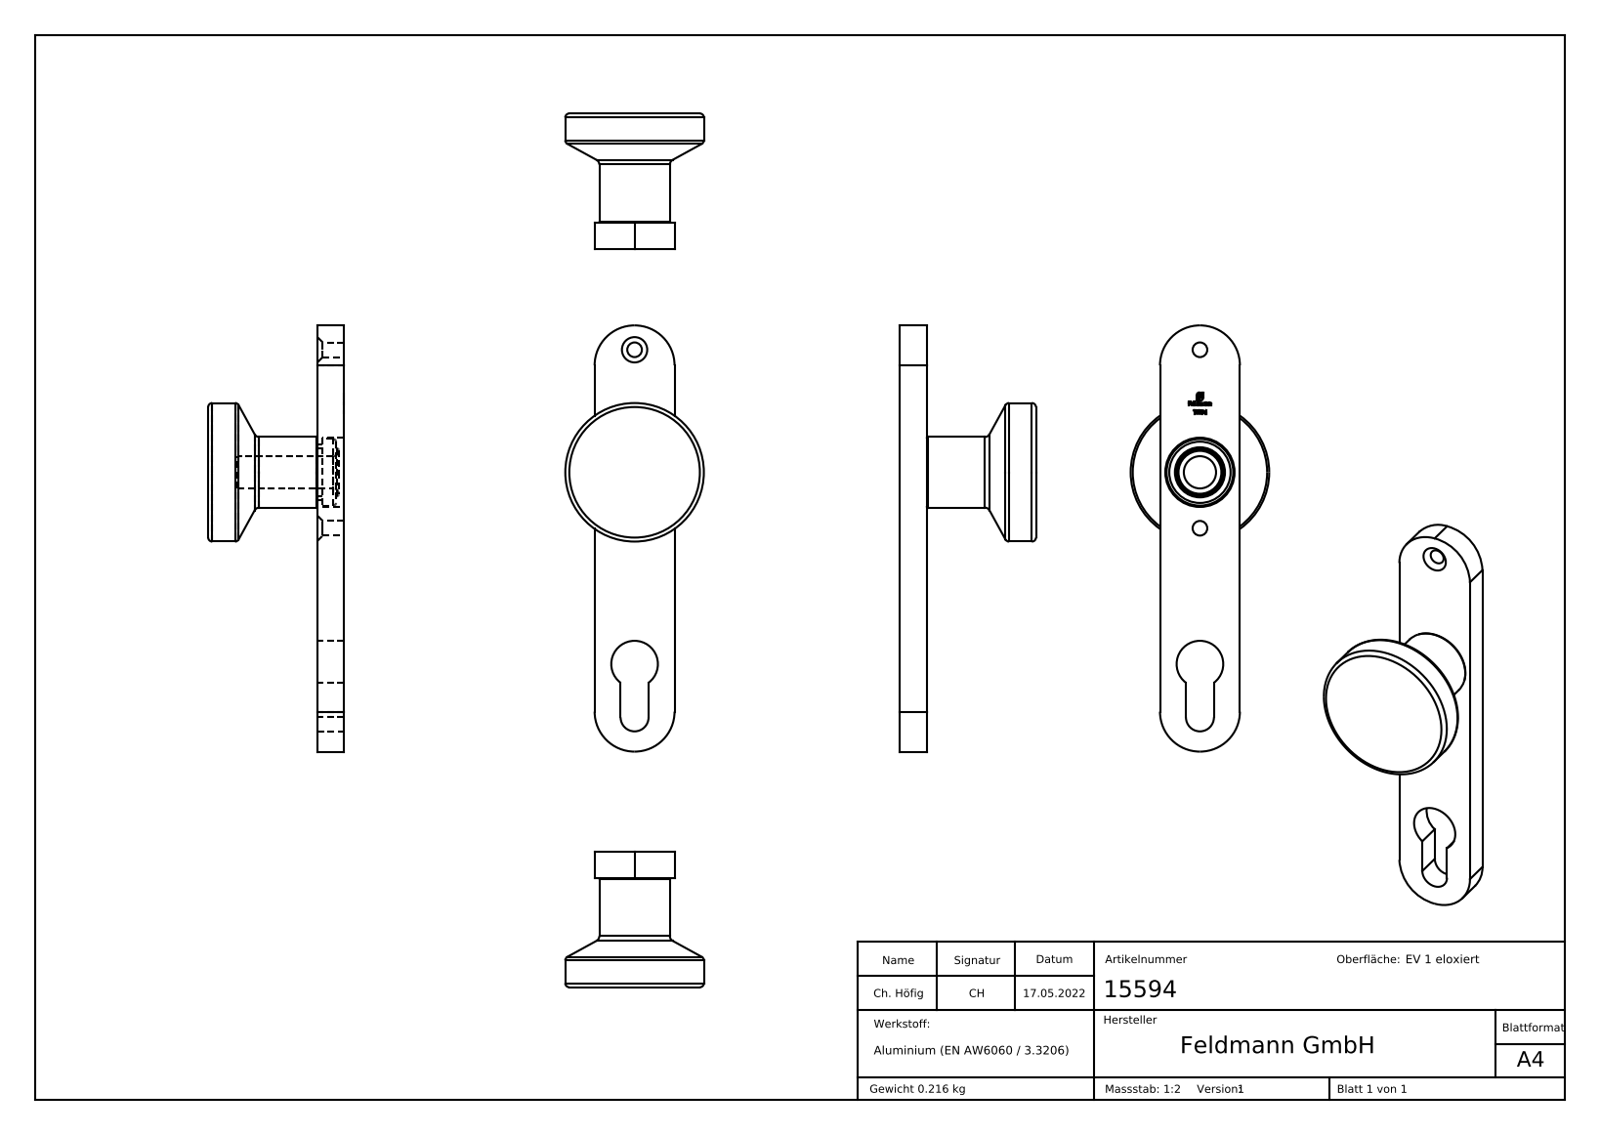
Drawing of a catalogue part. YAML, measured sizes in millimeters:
part_name: "15594 Teil1_15594 Teil1; 15594; 15594 Teil2_15594 Teil2"
step_written_by: "SolidWorks 2018 (CONFIG_CONTROL_DESIGN)"
units: millimeters
bodies: {solids: 2, faces: 261, planar: 142, cylindrical: 15, other: 104}
overall_size: [160, 52, 51]
volume: 79999
surface_area: 23536
round_holes:
  - {diameter: 5.5, count: 2}
  - {diameter: 12.1, count: 1}
  - {diameter: 17.5, count: 1}
  - {diameter: 21, count: 1}
  - {diameter: 26, count: 1}
round_bosses_or_shafts:
  - {diameter: 52, count: 1}
  - {diameter: 26.5, count: 1}
  - {diameter: 25, count: 1}
  - {diameter: 17.8, count: 1}
partial_cylinders:
  - {radius: 15, count: 2}
  - {radius: 5.25, count: 1}
face_to_face_distances: [10, 51, 41, 30, 2, 8, 43, 9.75, 20.25, 3]
hole_center_spacings: [21, 46, 51, 67, 72, 118]
